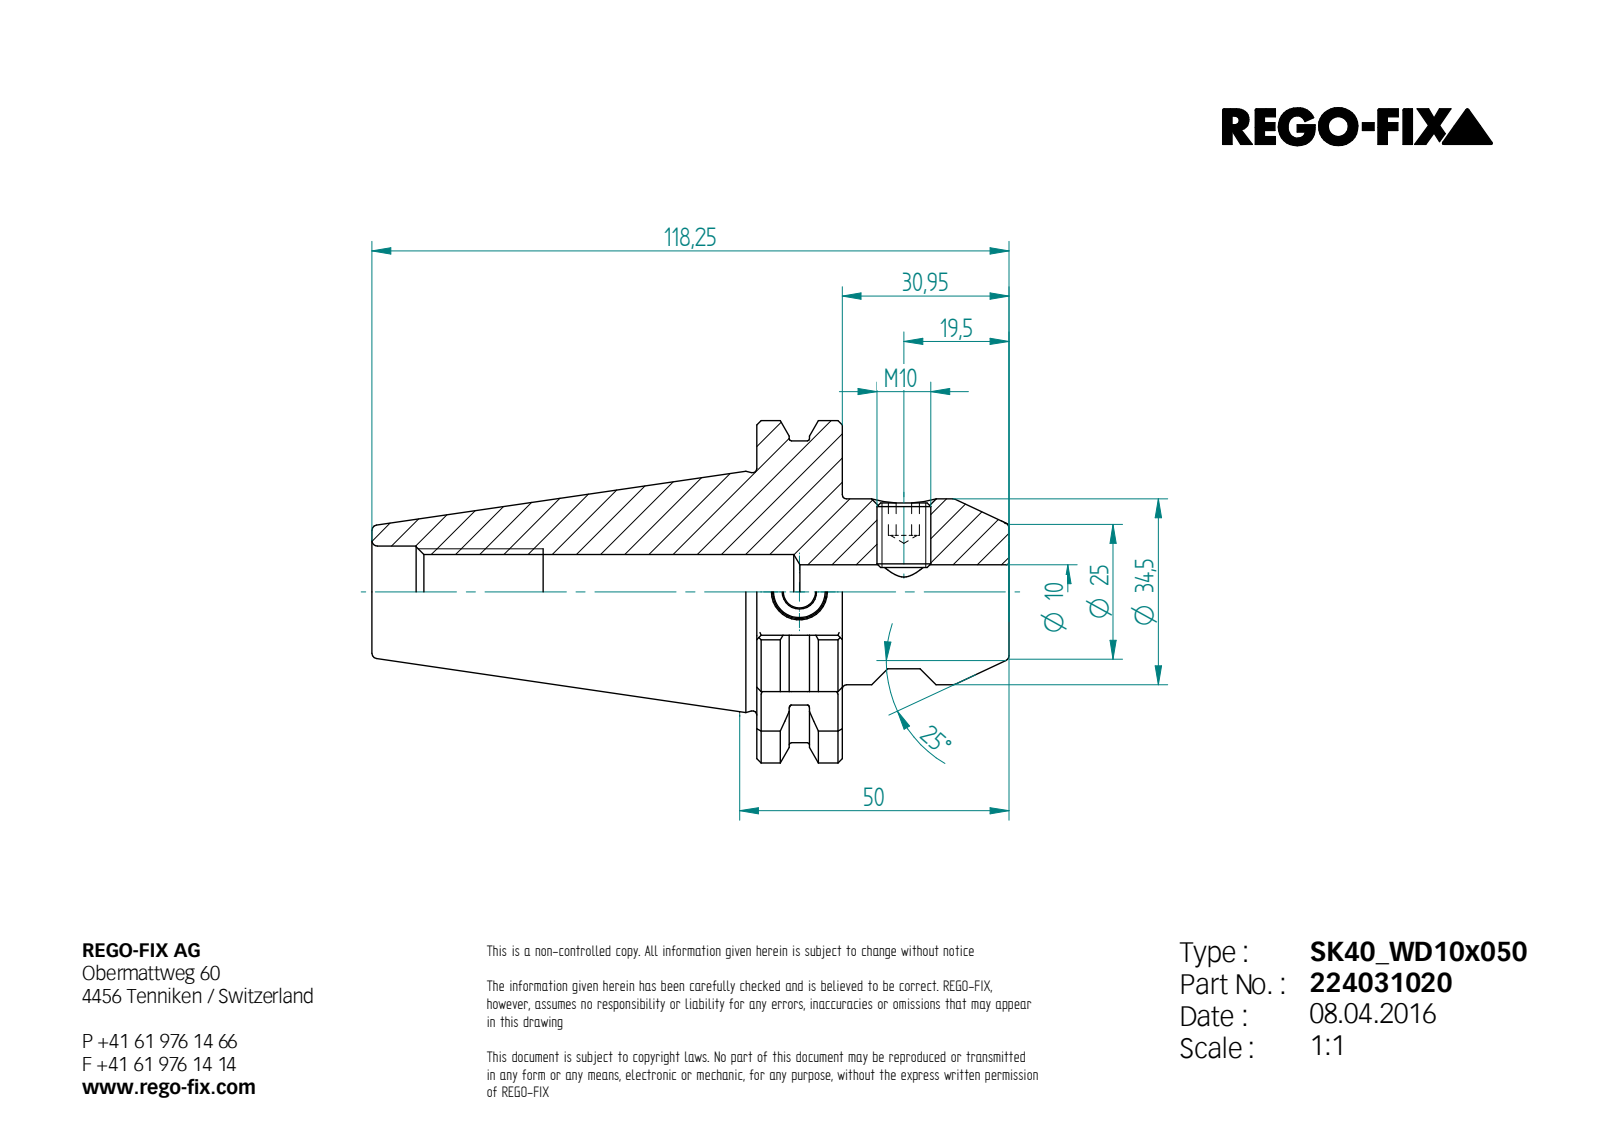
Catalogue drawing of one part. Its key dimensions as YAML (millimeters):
step_written_by: "Unknown (AUTOMOTIVE_DESIGN)"
units: millimeters
bodies: {solids: 2, faces: 127, planar: 58, cylindrical: 31, other: 38}
overall_size: [118.25, 63.55, 61.01]
volume: 123597
surface_area: 24872
round_holes:
  - {diameter: 10, count: 2}
  - {diameter: 6, count: 1}
  - {diameter: 8.38, count: 1}
  - {diameter: 13.84, count: 1}
  - {diameter: 17, count: 1}
round_bosses_or_shafts:
  - {diameter: 34.5, count: 1}
  - {diameter: 10, count: 1}
partial_cylinders:
  - {radius: 0.5, count: 13}
  - {radius: 28, count: 1}
  - {radius: 31.77, count: 1}
face_to_face_distances: [15.85, 46.8, 30.95, 47.3, 16.1, 22.35, 71.45, 87.3, 118.25, 6.25]
